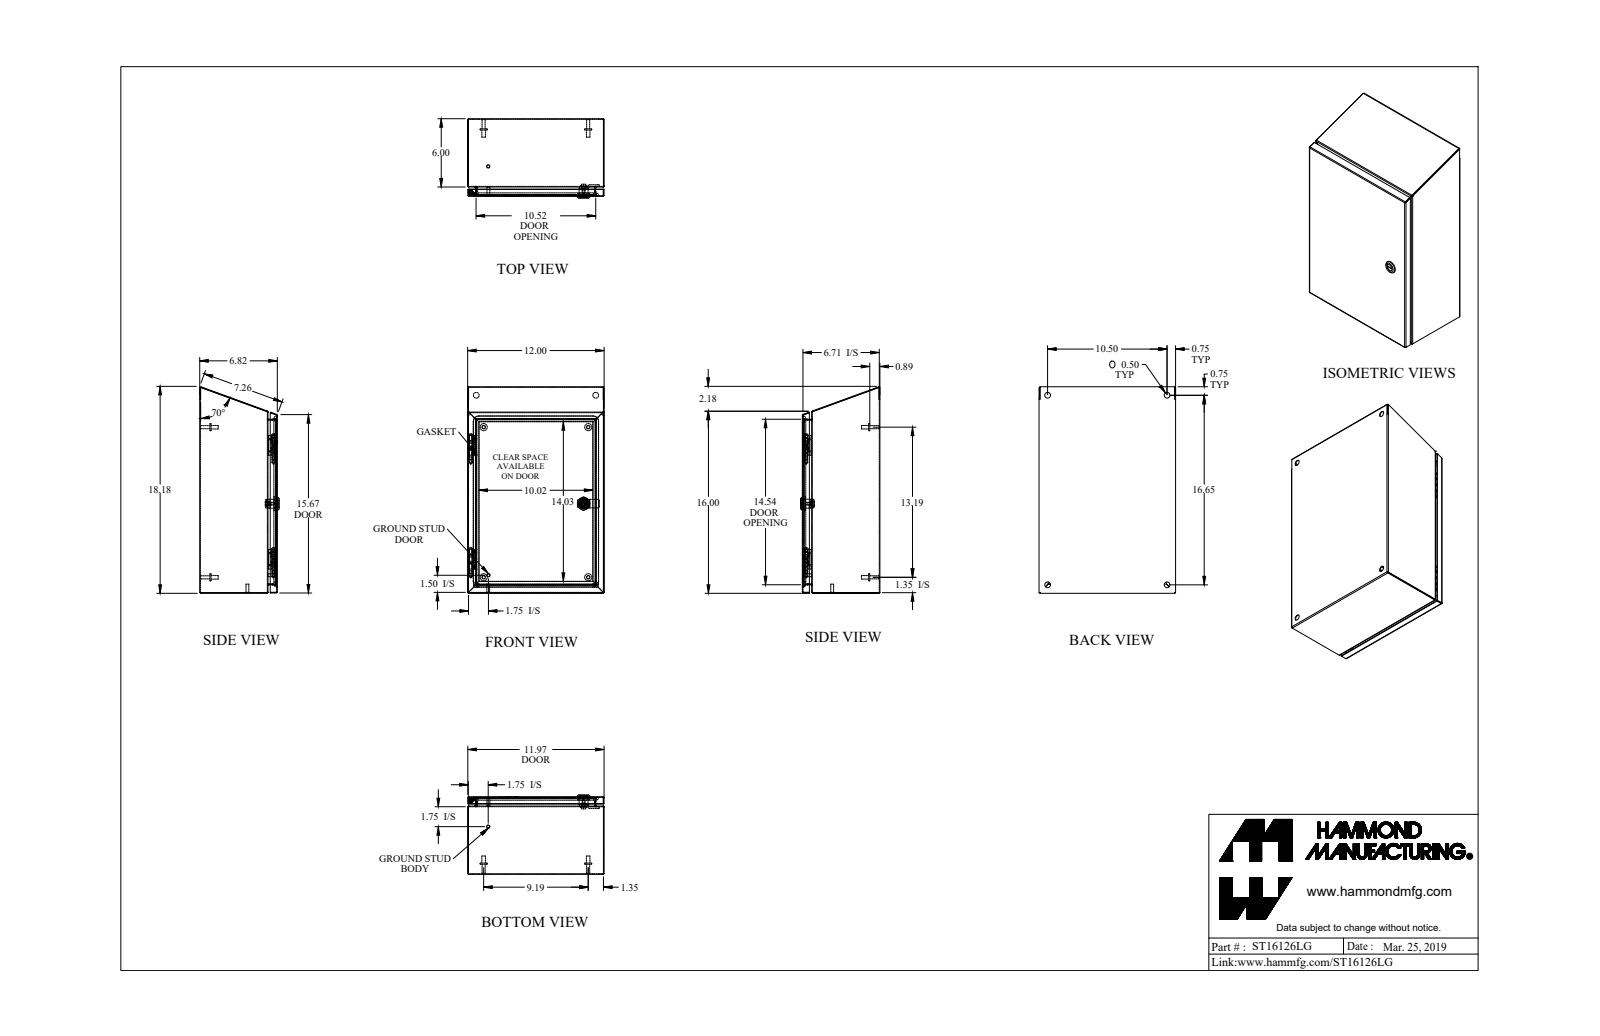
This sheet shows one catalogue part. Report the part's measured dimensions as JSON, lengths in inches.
{"part_name": "ST16126LG", "step_written_by": "SolidWorks 2018 (AUTOMOTIVE_DESIGN)", "units": "inches", "bodies": {"solids": 21, "faces": 632, "planar": 303, "cylindrical": 197, "other": 132}, "overall_size": [18.147, 12, 6.982], "volume_in3": 55.26, "surface_area_in2": 1864, "round_holes": [[0.5, 4], [0.172, 1], [0.232, 1], [0.24, 1], [0.242, 1], [0.625, 1], [0.785, 1]], "round_bosses_or_shafts": [[0.625, 4], [0.313, 4], [0.27, 4], [0.281, 2], [0.25, 2], [1.1, 1], [0.525, 1], [0.455, 1]], "partial_cylinders_radius": [[0.029, 21], [0.086, 21], [0.25, 11], [0.006, 4], [0.062, 4], [0.499, 4], [0.125, 2], [0.021, 1]], "face_to_face_distances": [0.057, 6.765, 6.708, 11.943, 6.822, 11.886, 12, 5.943, 0.822, 6], "hole_center_spacings": [10.5, 16.646, 19.681, 7.206, 9.578, 11.83, 13.407]}
